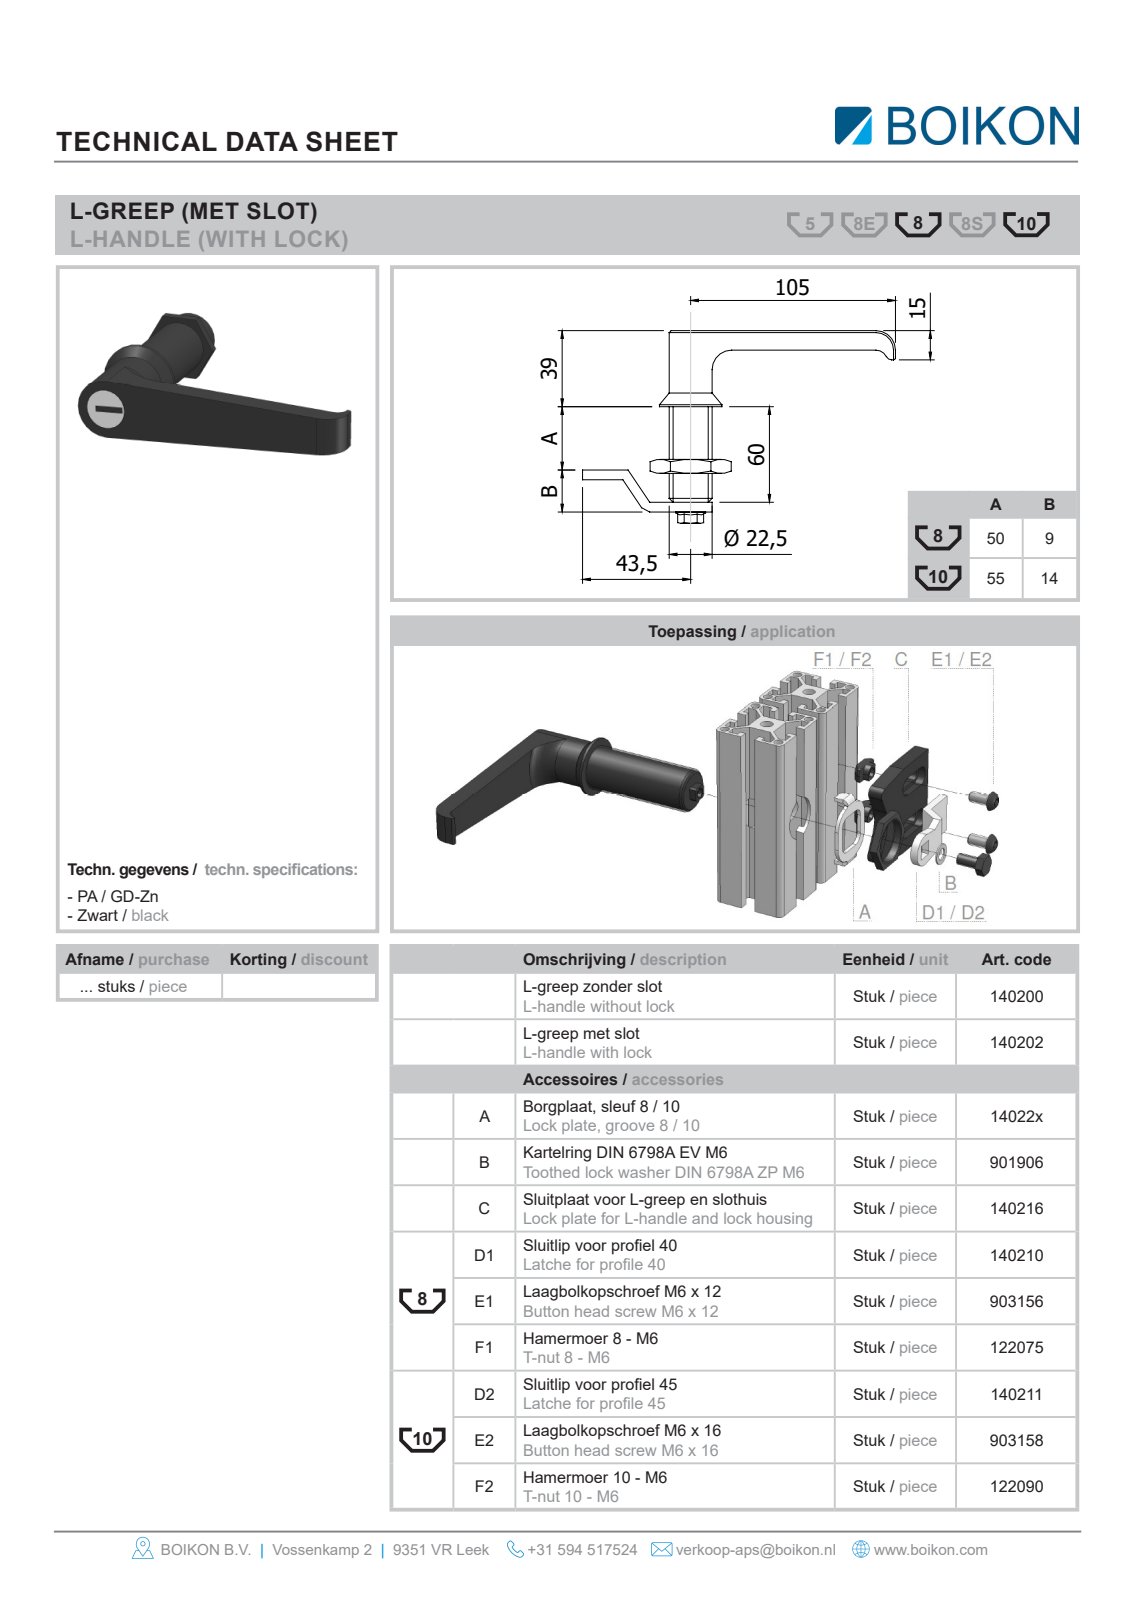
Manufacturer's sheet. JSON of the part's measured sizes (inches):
{"part_name": "Root; 140202Deurgreep met slotBOIKON; 140211Sluitlip 45 profielBOIKON; 901906Kartelring DIN 6798A EV M6Washers0 (+3 more)", "step_written_by": "HiCAD 2013 1802.4 Build 509 (AUTOMOTIVE_DESIGN)", "units": "inches", "bodies": {"solids": 8, "faces": 128, "planar": 93, "cylindrical": 33, "other": 2}, "overall_size": [5.787, 4.252, 1.504], "volume_in3": 4.225, "surface_area_in2": 30.82, "round_holes": [[0.252, 1], [0.669, 1]], "round_bosses_or_shafts": [[1.26, 1], [0.984, 1], [0.886, 1], [0.661, 1], [0.433, 1], [0.236, 1]], "partial_cylinders_radius": [[0.197, 5], [0.394, 5], [0.079, 4], [0.039, 3], [0.118, 2], [0.177, 1]], "face_to_face_distances": [0.394, 0.157, 0.197, 0.512, 3.307, 0.315, 0.354, 0.591, 0.079, 0.039]}
